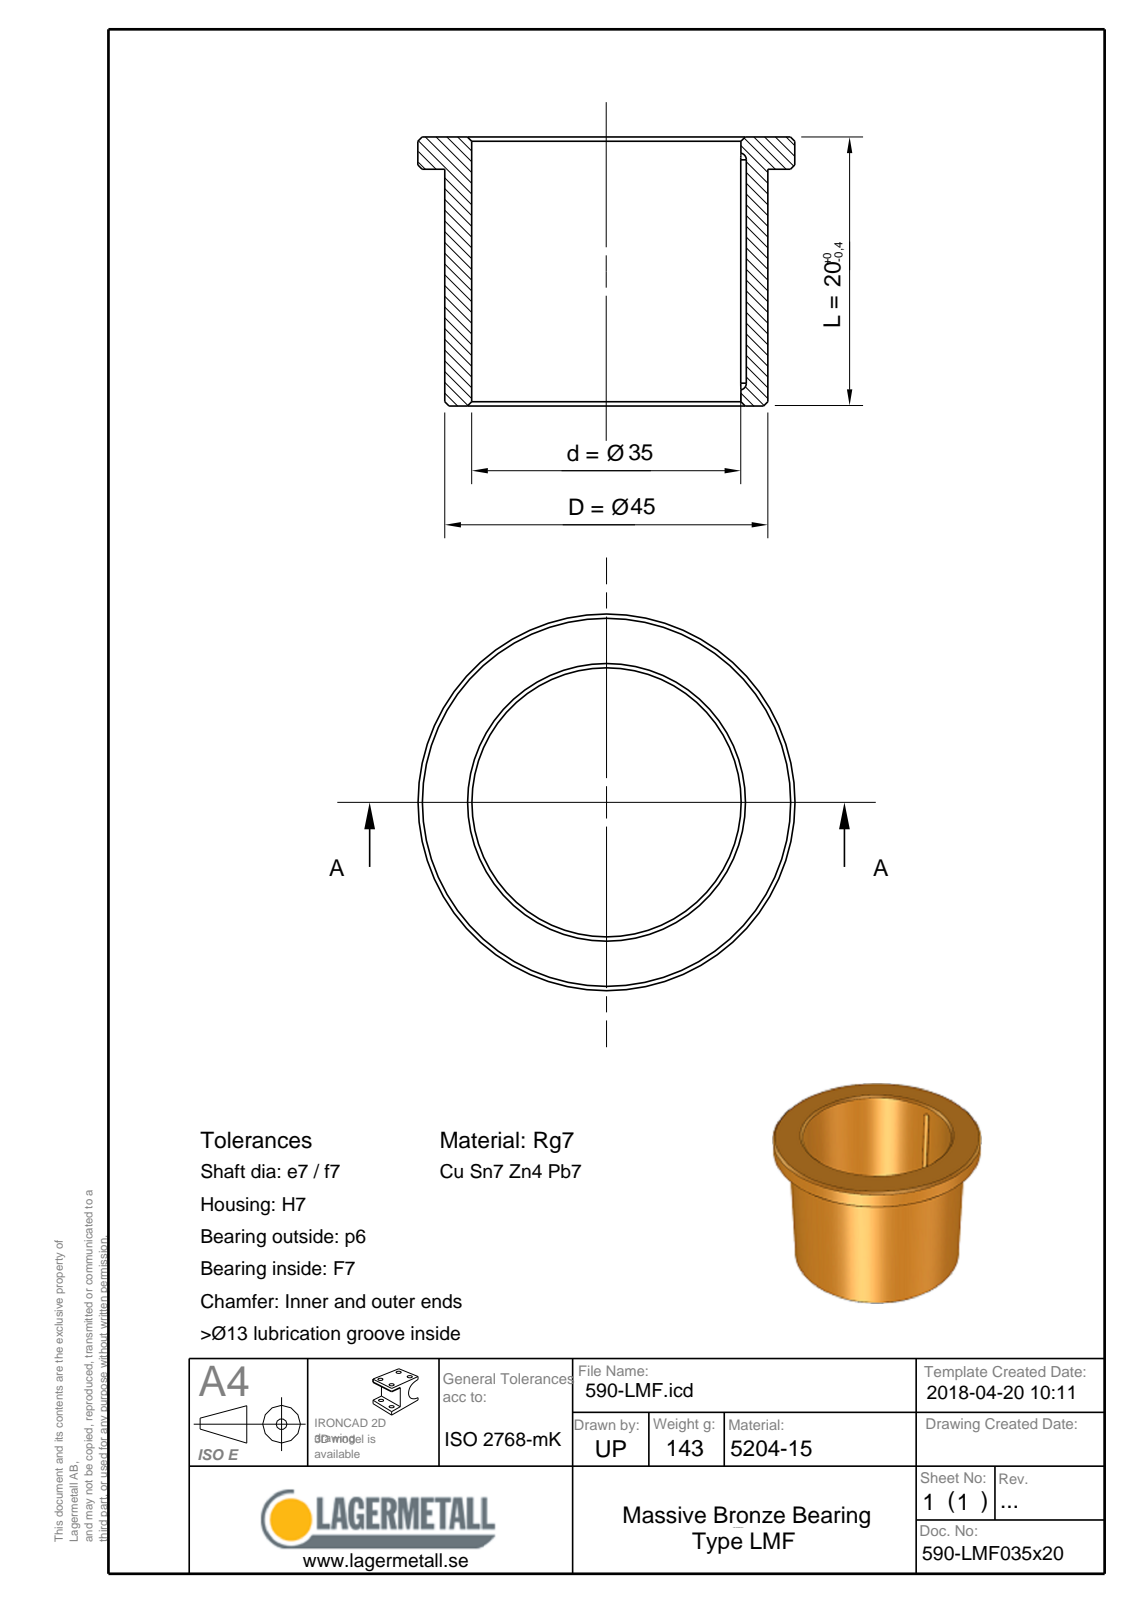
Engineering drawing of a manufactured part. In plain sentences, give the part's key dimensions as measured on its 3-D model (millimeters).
The part is named "590-LMF035x20". Its 3-D file was written by "Spatial InterOp 3D (CONFIG_CONTROL_DESIGN)". It is 1 solid with 16 faces: 4 planar, 5 cylindrical and 7 other. Overall it measures 55 by 55 by 20 millimeters. Its volume is 16 243 cubic millimeters and its surface area 7 694 square millimeters. Round holes: 1 of diameter 35. Round bosses or shafts: 1 of diameter 55, 1 of diameter 45. Partial cylindrical surfaces (rounded edges, fillets, slot ends): 2 of radius 1.25. The main face-to-face distances are 5, 15, 20.
